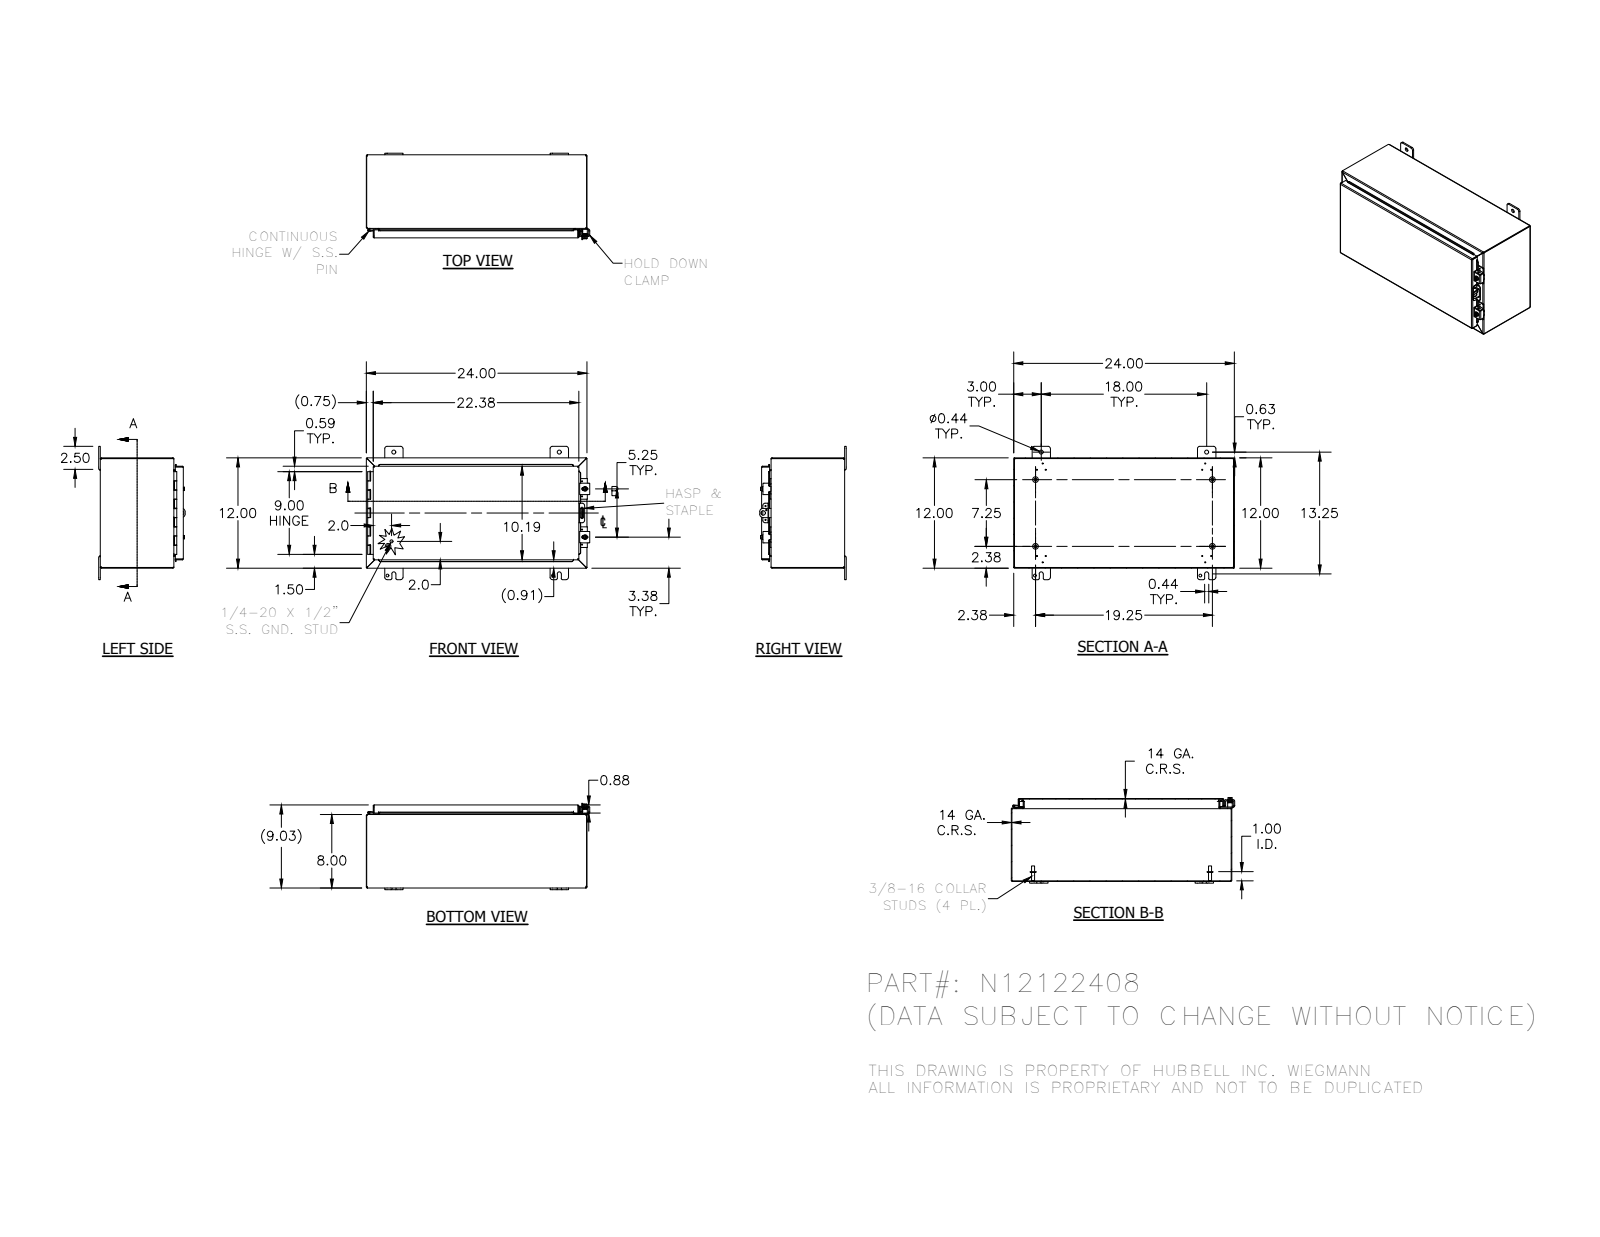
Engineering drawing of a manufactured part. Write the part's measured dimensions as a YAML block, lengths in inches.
part_name: "N12122408; 34840; 38420; N12122408BKP (+8 more)"
step_written_by: "Autodesk Inventor 2012 (AUTOMOTIVE_DESIGN)"
units: inches
bodies: {solids: 27, faces: 880, planar: 467, cylindrical: 296, other: 117}
overall_size: [24.311, 14.5, 9.41]
volume: 108.3
surface_area: 2795
round_holes:
  - {diameter: 0.12, count: 12}
  - {diameter: 0.11, count: 7}
  - {diameter: 0.313, count: 4}
  - {diameter: 0.438, count: 4}
  - {diameter: 0.211, count: 2}
  - {diameter: 0.281, count: 2}
  - {diameter: 0.3, count: 2}
  - {diameter: 0.125, count: 1}
  - {diameter: 0.156, count: 1}
  - {diameter: 0.5, count: 1}
round_bosses_or_shafts:
  - {diameter: 0.625, count: 4}
  - {diameter: 0.33, count: 4}
  - {diameter: 0.25, count: 4}
  - {diameter: 0.52, count: 2}
  - {diameter: 0.5, count: 2}
  - {diameter: 0.35, count: 2}
  - {diameter: 0.115, count: 2}
  - {diameter: 0.337, count: 1}
partial_cylinders:
  - {radius: 0.03, count: 27}
  - {radius: 0.063, count: 25}
  - {radius: 0.125, count: 25}
  - {radius: 0.25, count: 25}
  - {radius: 0.031, count: 23}
  - {radius: 0.105, count: 23}
  - {radius: 0.07, count: 8}
  - {radius: 0.1, count: 4}
face_to_face_distances: [0.074, 8.959, 11.926, 8.885, 9.033, 12, 11.852, 23.926, 7.926, 1.033]
hole_center_spacings: [18, 0.759, 0.94, 0.969, 1.995, 9.38, 9.43, 10.071]
